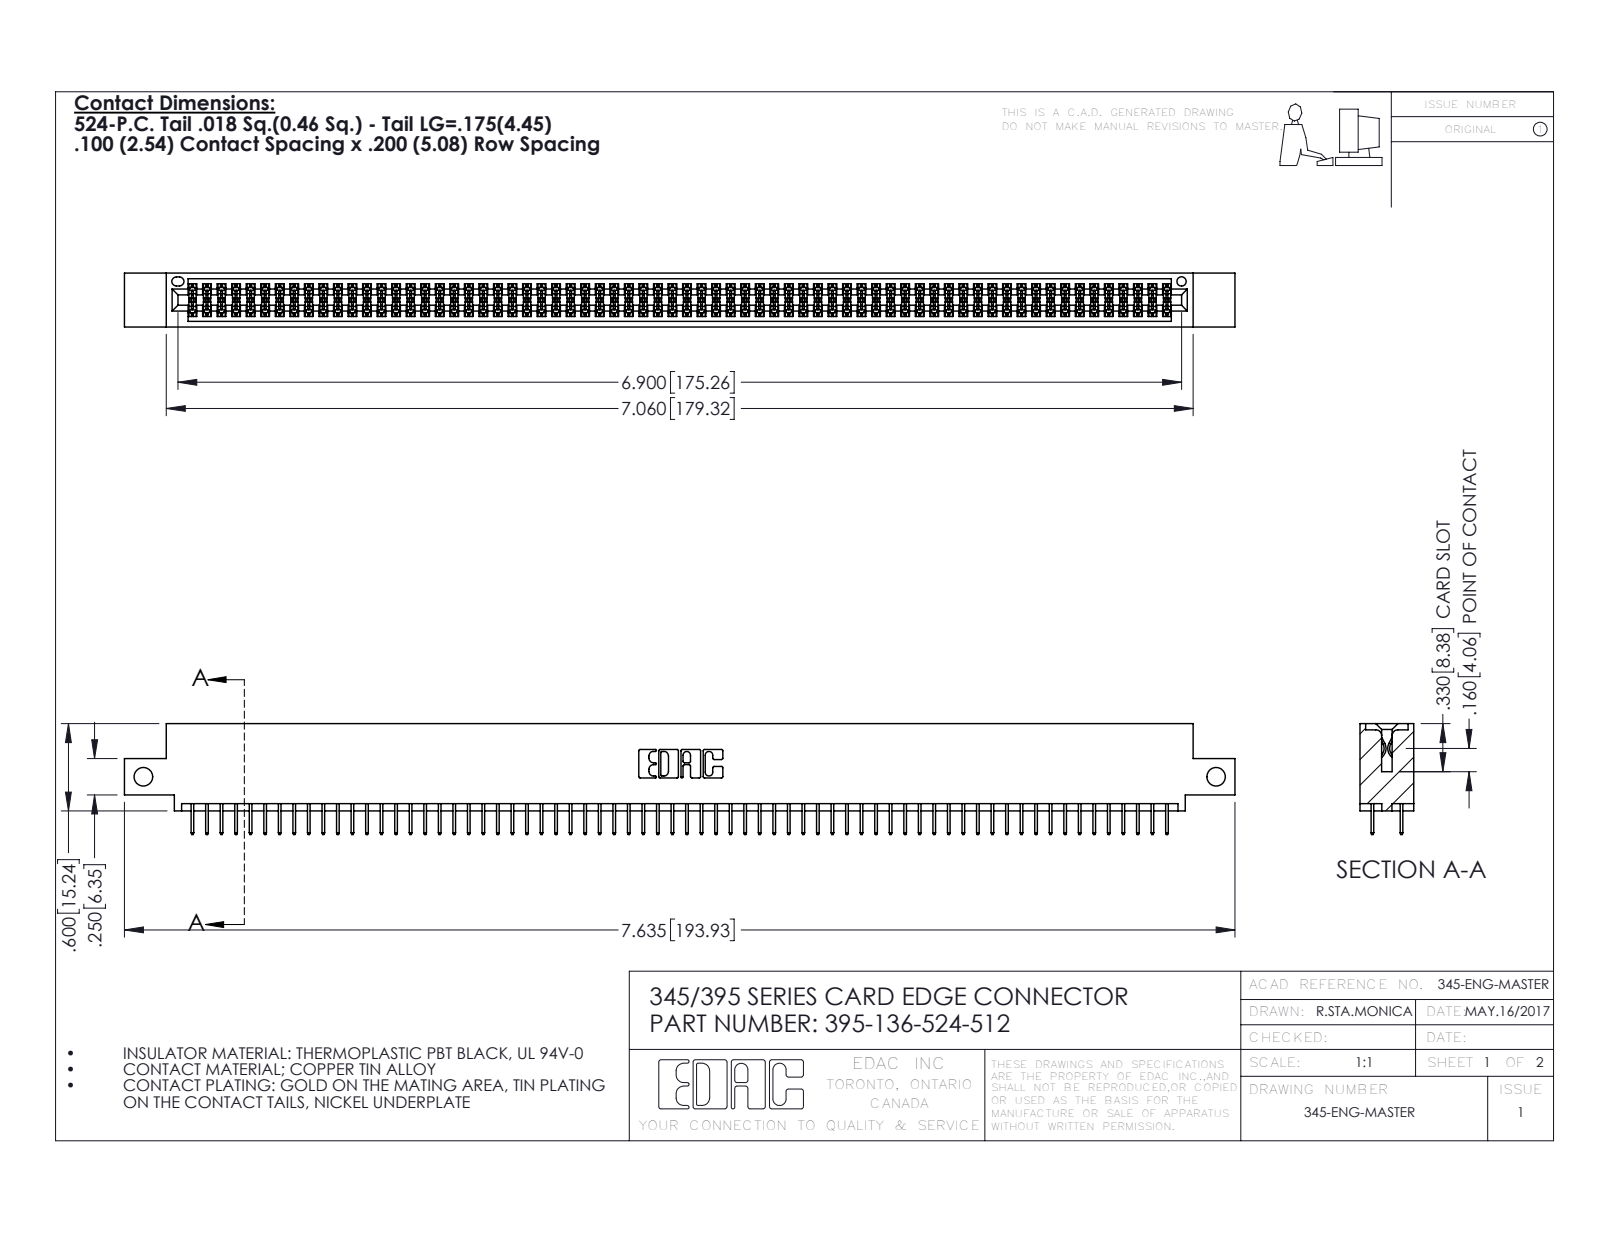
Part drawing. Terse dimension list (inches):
name: 345 Part_0.110 Offset - Side Mount; 345-292-001_345-293-124; 395-136-524-512
written by: SolidWorks 2016 (CONFIG_CONTROL_DESIGN)
unit: in
bodies: 137 solids, 7474 faces (5388 planar, 2086 cylindrical, 0 other)
size: 7.635 × 0.762 × 0.37
volume: 1.142 in³; area: 42.75 in²
holes: 2× ⌀0.128, 1× ⌀0.064
rounds: 204× R0.006, 22× R0.01, 6× R0.007, 6× R0.031, 3× R0.026, 2× R0.014, 2× R0.019, 2× R0.022
face distances: 0.072, 0.298, 0.2, 0.37, 0.098, 0.272, 0.025, 0.225, 0.072, 0.175
hole spacings: 7.375
